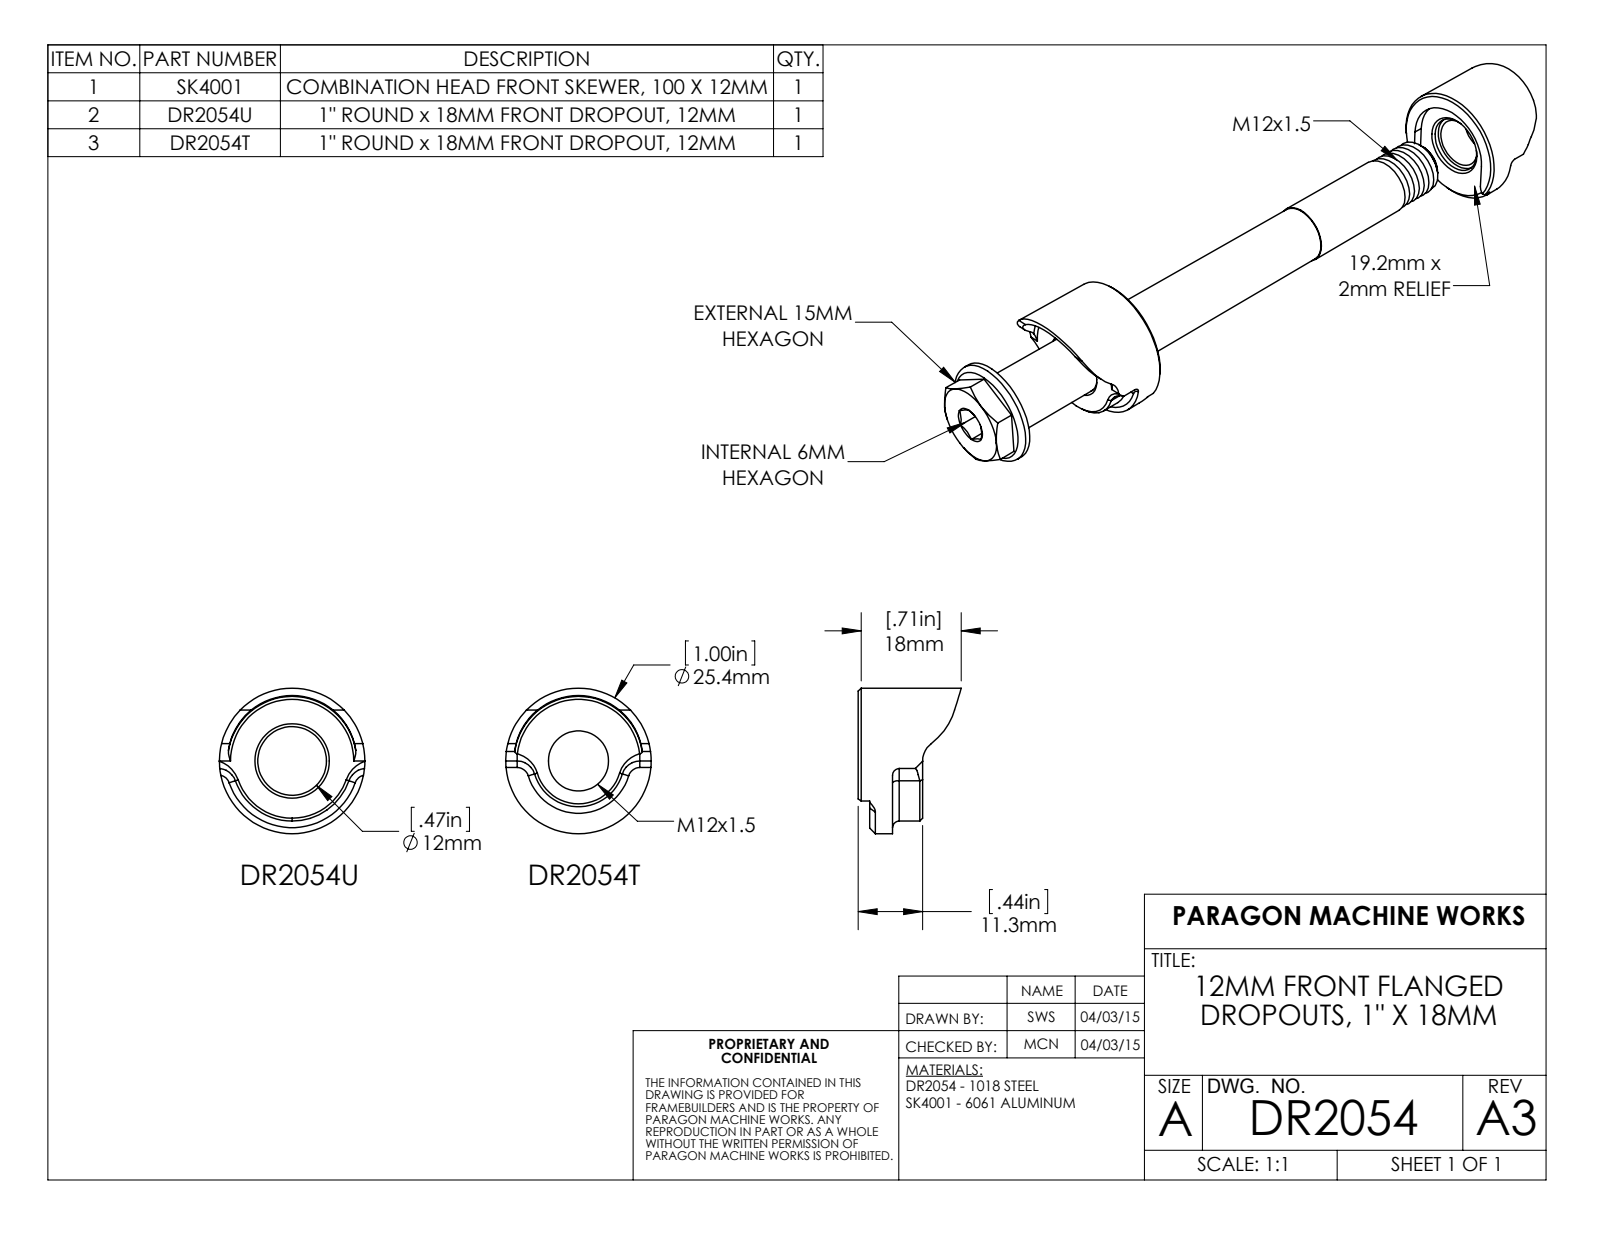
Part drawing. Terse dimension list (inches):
name: SK4001; DR2054U; DR2054T; DR2054
written by: SolidWorks 2015 (AUTOMOTIVE_DESIGN)
unit: in
bodies: 3 solids, 129 faces (38 planar, 38 cylindrical, 53 other)
size: 5.197 × 1 × 1
volume: 1.285 in³; area: 16.04 in²
holes: 1× ⌀0.472
bosses: 1× ⌀1, 1× ⌀0.787, 1× ⌀0.471, 1× ⌀0.46
rounds: 4× R0.125, 2× R0.098, 2× R0.15, 2× R0.456, 1× R0.045, 1× R0.315, 1× R0.378, 1× R0.413
face distances: 4.301, 0.364, 0.236, 0.443, 0.079, 4.459, 4.222, 3.858, 3.937, 0.157
